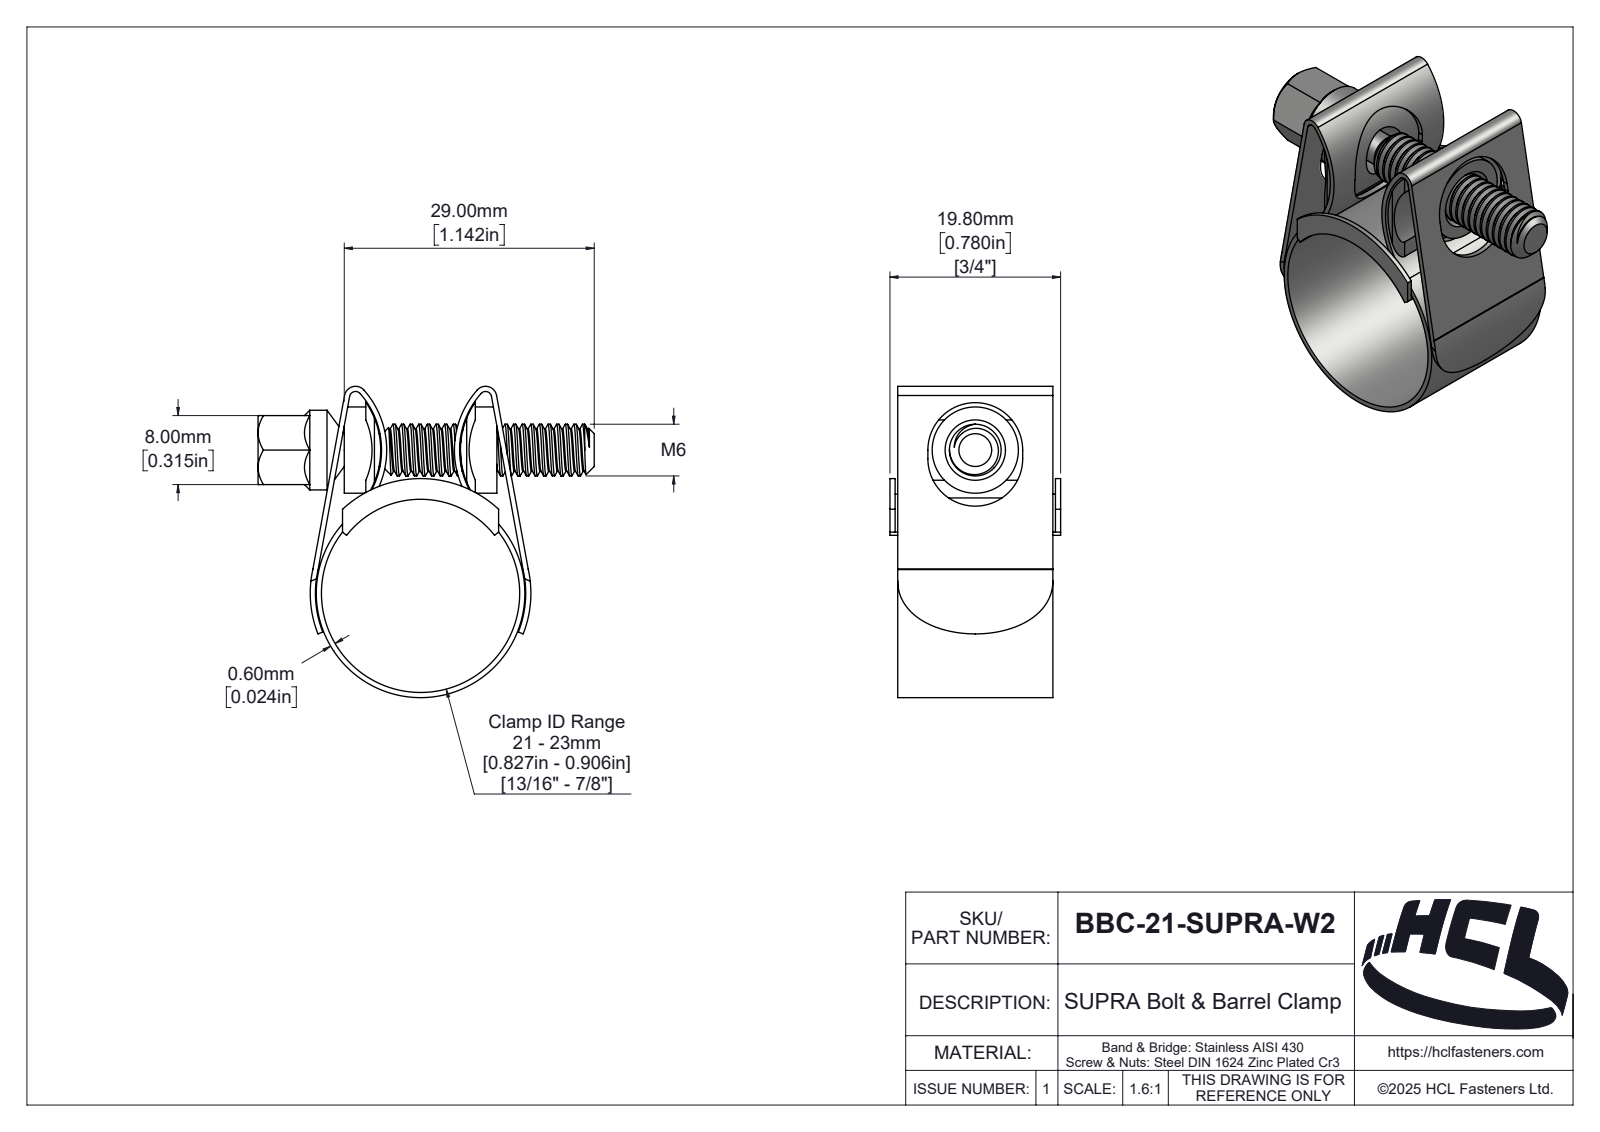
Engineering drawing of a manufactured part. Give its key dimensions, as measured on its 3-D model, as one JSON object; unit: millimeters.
{"part_name": "BBC-21-SUPRA-W2", "step_written_by": "SolidWorks 2025 (AUTOMOTIVE_DESIGN)", "units": "millimeters", "bodies": {"solids": 5, "faces": 283, "planar": 44, "cylindrical": 159, "other": 80}, "overall_size": [39, 36.1, 19.8], "volume_mm3": 3327, "surface_area_mm2": 7840, "round_holes": [[23, 1]], "round_bosses_or_shafts": [[10, 1], [9.24, 1], [6, 1], [3.8, 1]], "partial_cylinders_radius": [[1, 4], [0.7, 2], [1.3, 2], [2, 2], [2.6, 2], [5.5, 2], [8.79, 2], [9.79, 2]], "face_to_face_distances": [0.6, 0.9, 18.9, 18, 2.5, 15.2, 8, 19.2, 18.3, 17.7]}
